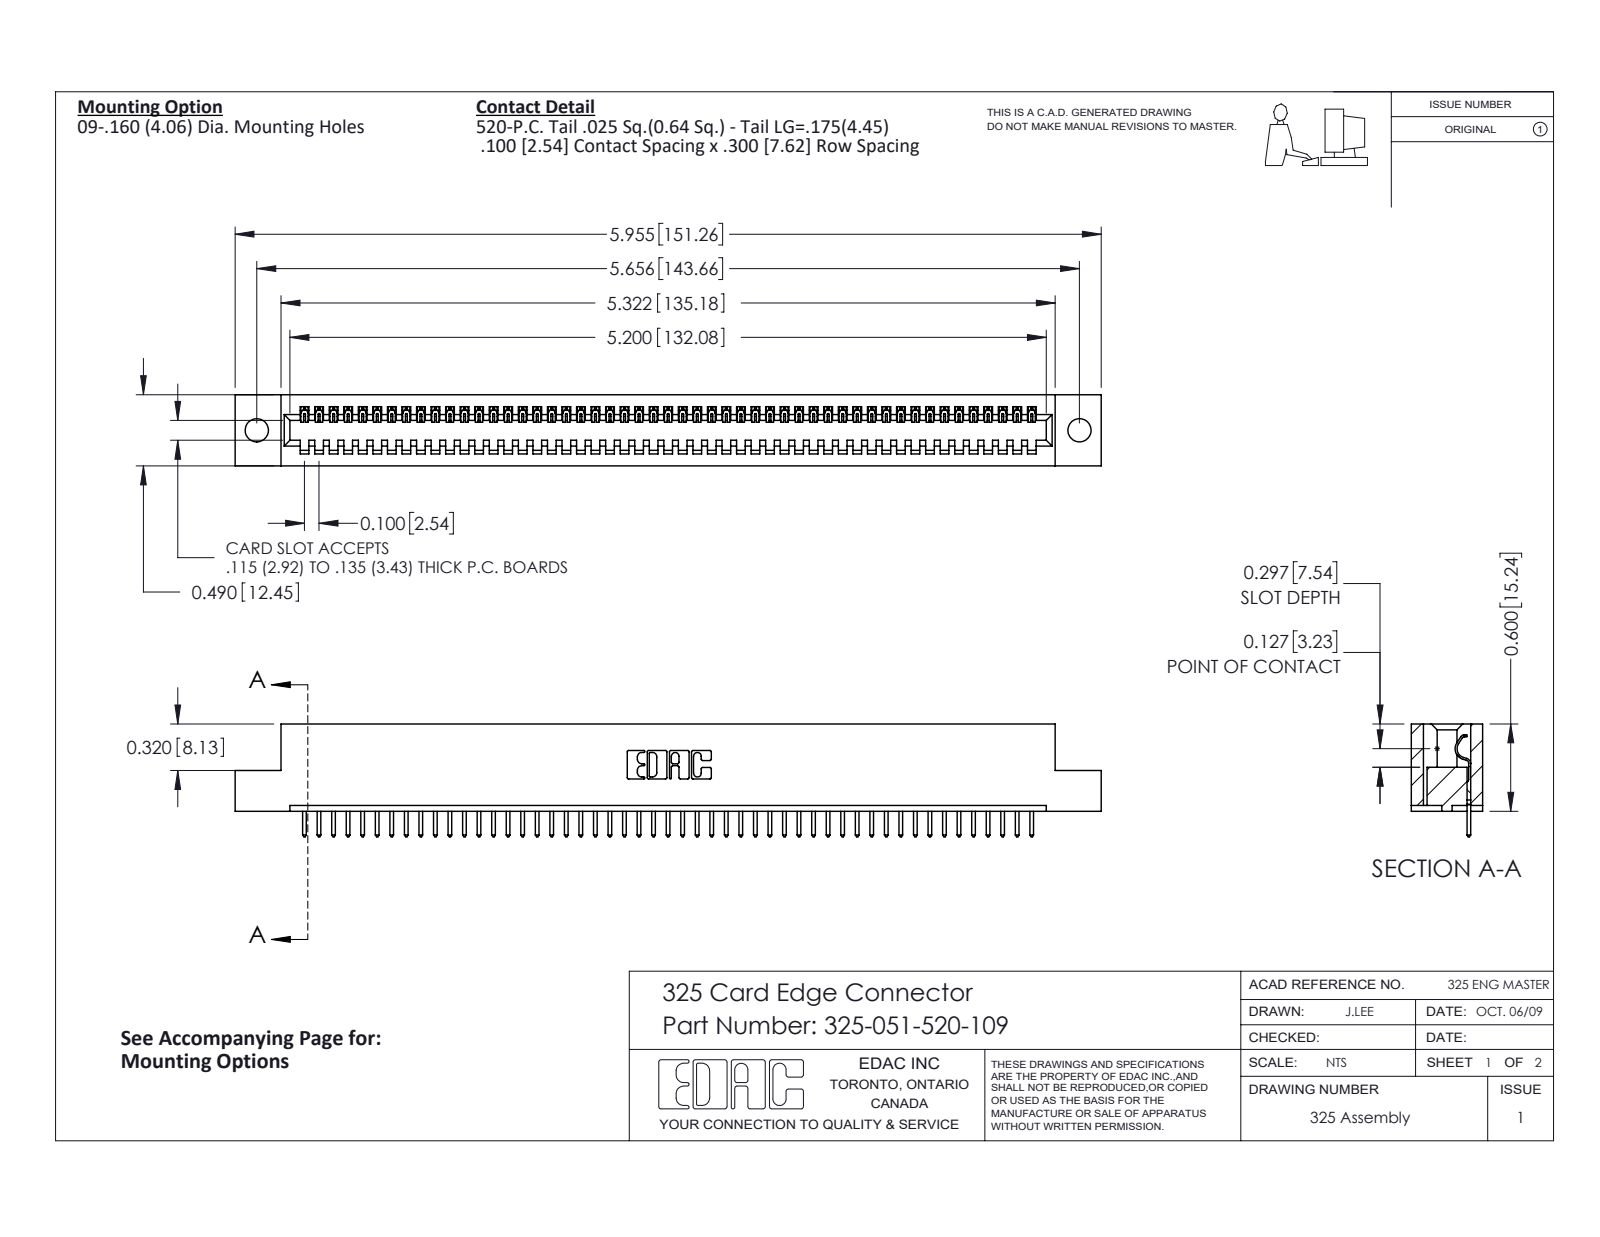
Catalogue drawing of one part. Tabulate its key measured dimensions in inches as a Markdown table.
| quantity | value |
| --- | --- |
| part name | 325-292-001_325-293-120; 325-051-520-109; 325 Part_.160 TH |
| STEP written by | SolidWorks 2016 (CONFIG_CONTROL_DESIGN) |
| units | inches |
| bodies | 52 solids, 3072 faces (2212 planar, 860 cylindrical, 0 other) |
| overall size | 5.955 × 0.775 × 0.49 |
| volume | 1.154 in³ |
| surface area | 31.27 in² |
| round holes (diameter × count) | 0.16 × 2 |
| partial cylindrical surfaces (radius × count) | 0.006 × 102, 0.01 × 102, 0.01 × 22, 0.007 × 6, 0.031 × 6, 0.026 × 3, 0.014 × 1, 0.022 × 1 |
| main face-to-face distances | 0.083, 0.407, 0.49, 0.3, 0.107, 0.383, 0.025, 0.325, 0.56, 0.263 |
| hole center spacings | 5.656 |
